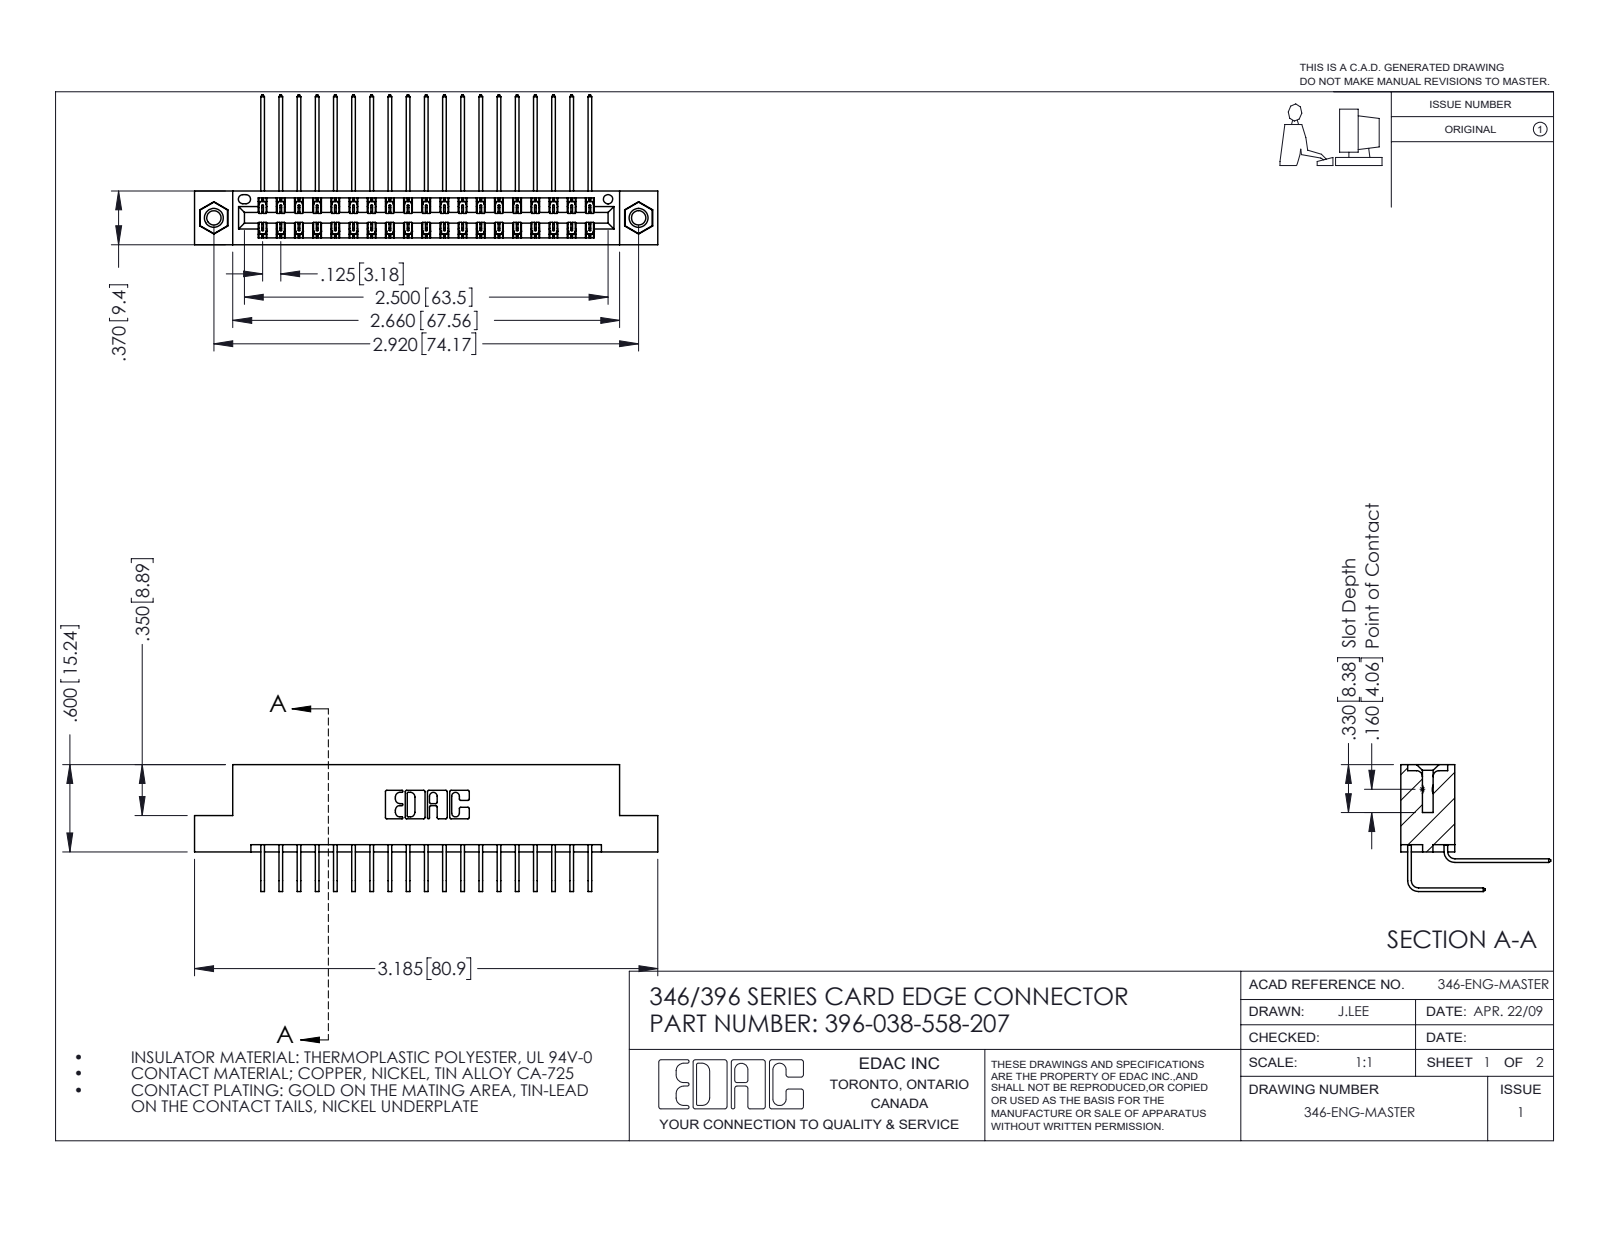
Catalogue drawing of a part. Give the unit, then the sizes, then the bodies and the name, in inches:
Units: inches
Overall size (bounding box): 3.185 × 1.03 × 0.873
Round holes (diameter × count): ⌀0.098 ×2, ⌀0.125 ×2, ⌀0.156 ×2, ⌀0.064 ×1
Round bosses / shafts (diameter × count): ⌀0.155 ×2
Partial cylindrical surfaces — rounded edges, fillets, slot ends (radius × count): R0.006 ×57, R0.01 ×22, R0.007 ×6, R0.031 ×6, R0.026 ×3, R0.014 ×2, R0.022 ×2, R0.024 ×2
Main face-to-face distances: 0.322, 0.048, 0.25, 0.025, 0.37, 0.298, 0.072, 0.275, 0.148, 0.222
Hole centre spacings: 0.246, 2.713, 2.92
Volume: 0.483 in³ · Surface area: 17.99 in²
Bodies: 41 solids, 2234 faces (1514 planar, 704 cylindrical, 16 other)
Part name (STEP PRODUCT): 346 Part_Flush Mounting Lugs - 0.156 Dia-TI; 345-250-001_345-250-005-103; 345-292-001_558 Tail - 2; 345-292-001_558 559 Tail - 1 (+1 more)
STEP written by: SolidWorks 2016 (CONFIG_CONTROL_DESIGN)
